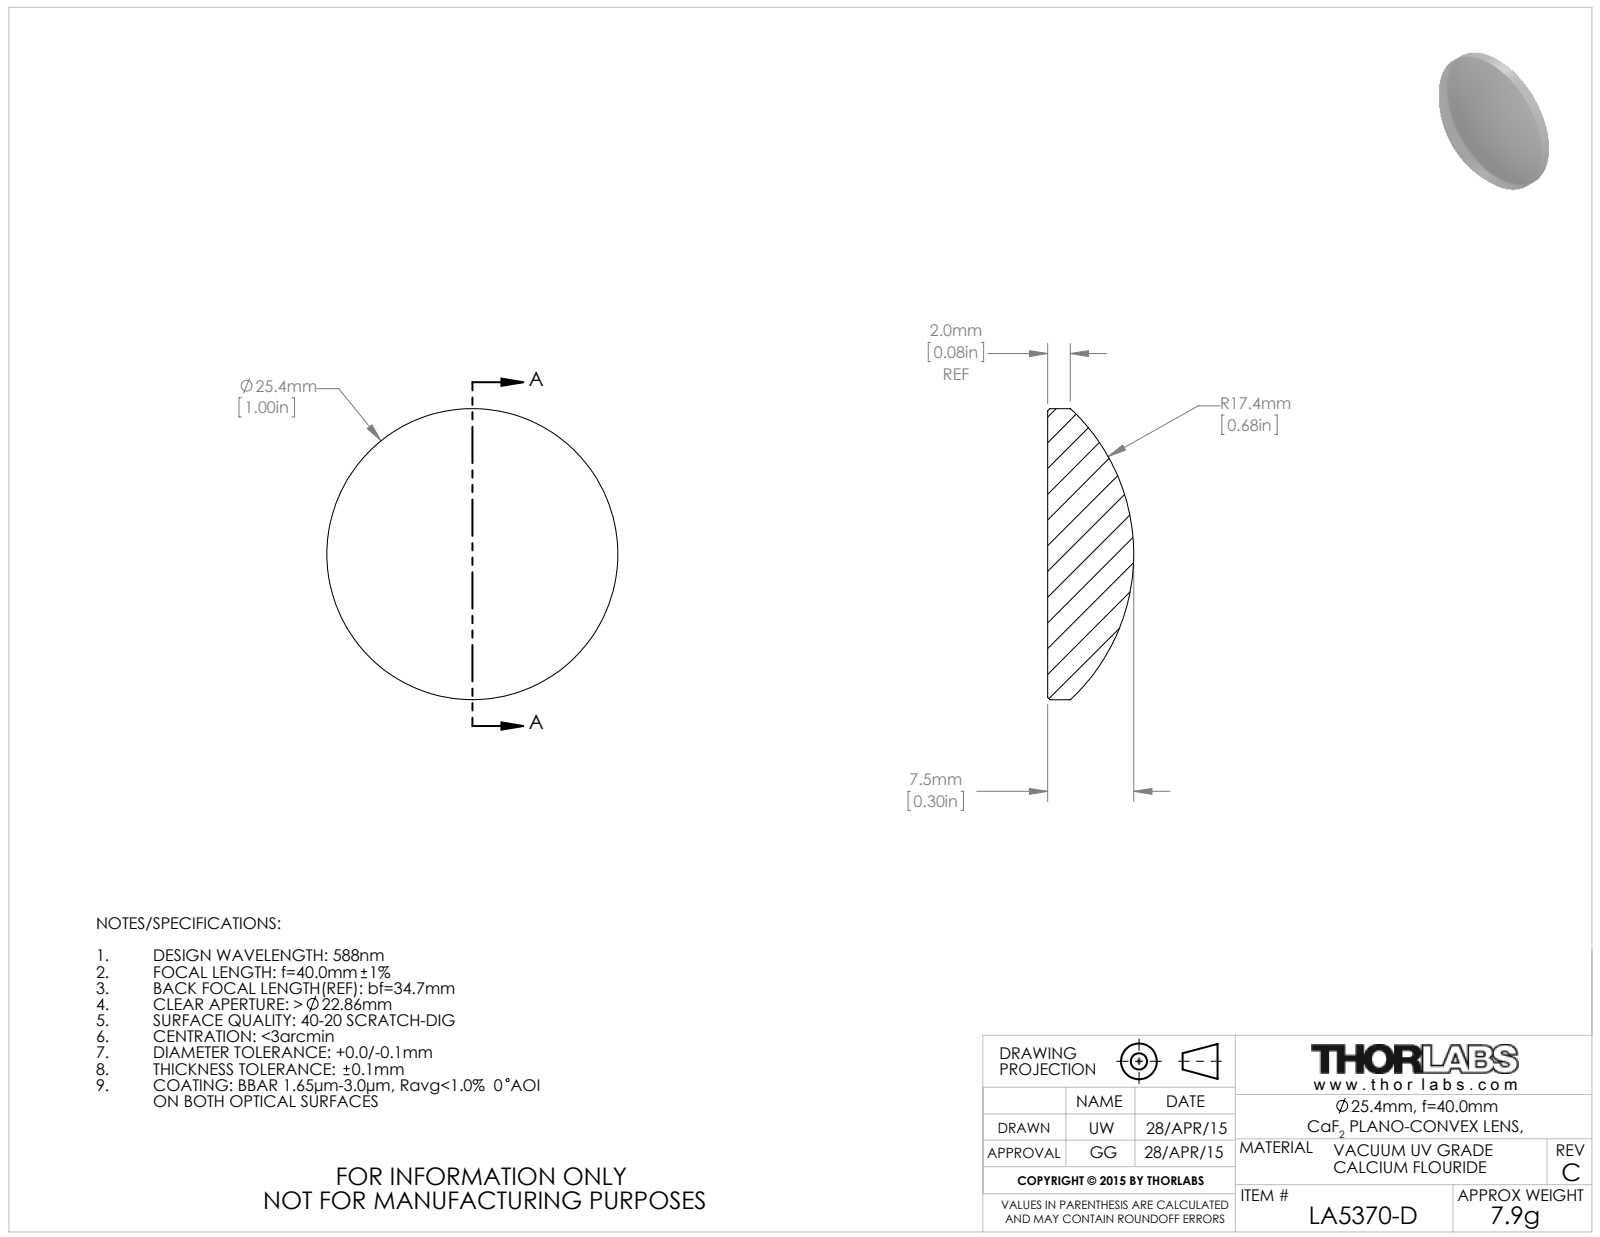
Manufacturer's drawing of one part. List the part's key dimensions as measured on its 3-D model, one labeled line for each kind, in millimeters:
Part name (STEP PRODUCT): 22959-E0W
STEP written by: SolidWorks 2014 (CONFIG_CONTROL_DESIGN)
Units: millimetres
Bodies: 1 solid, 7 faces (1 planar, 2 cylindrical, 4 other)
Overall size (bounding box): 25.4 × 25.4 × 7.52
Volume: 2 497 mm³ · Surface area: 1 259 mm²
Round bosses / shafts (diameter × count): ⌀25.4 ×1
